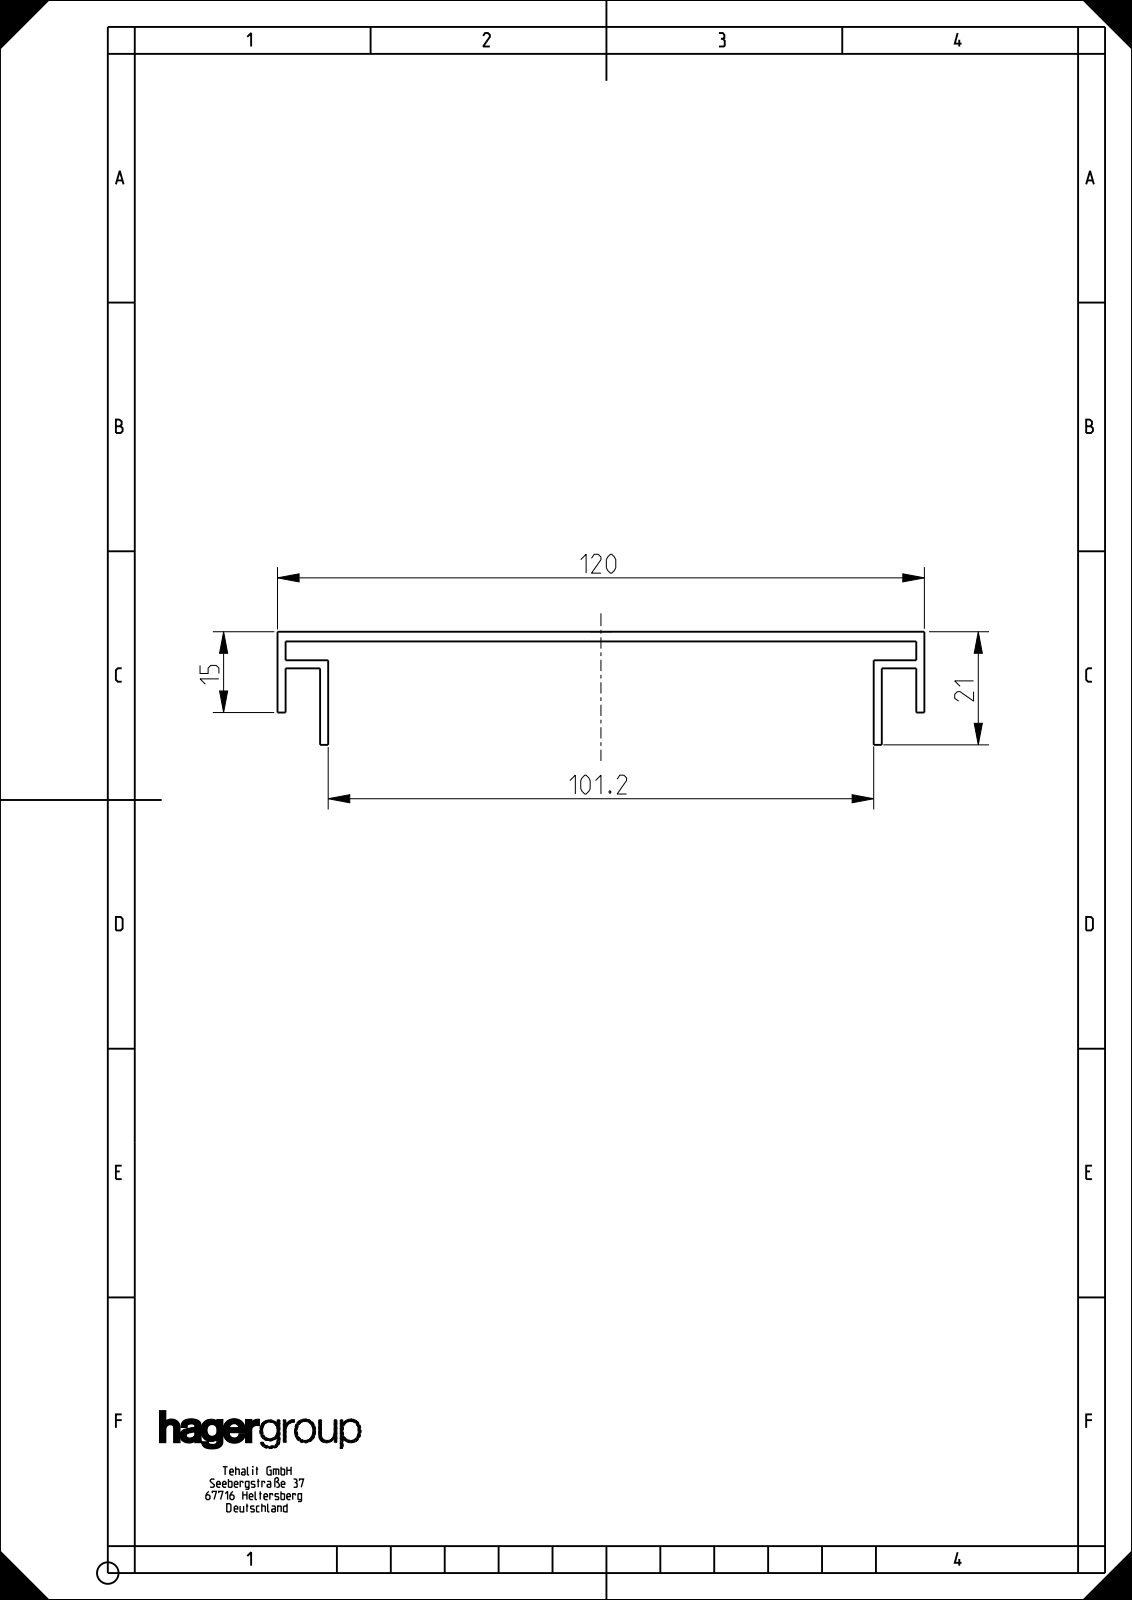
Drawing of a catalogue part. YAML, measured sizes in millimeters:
part_name: "BR1202"
step_written_by: "CREO PARAMETRIC BY PTC INC, 2022024 (AUTOMOTIVE_DESIGN)"
units: millimeters
bodies: {solids: 1, faces: 22, planar: 22, cylindrical: 0, other: 0}
overall_size: [2000, 120, 21]
volume: 643800
surface_area: 770244
face_to_face_distances: [1.8, 1.5, 110.6, 7.9, 9.4, 112.1, 102.7, 118.5, 6.4, 109.1]
